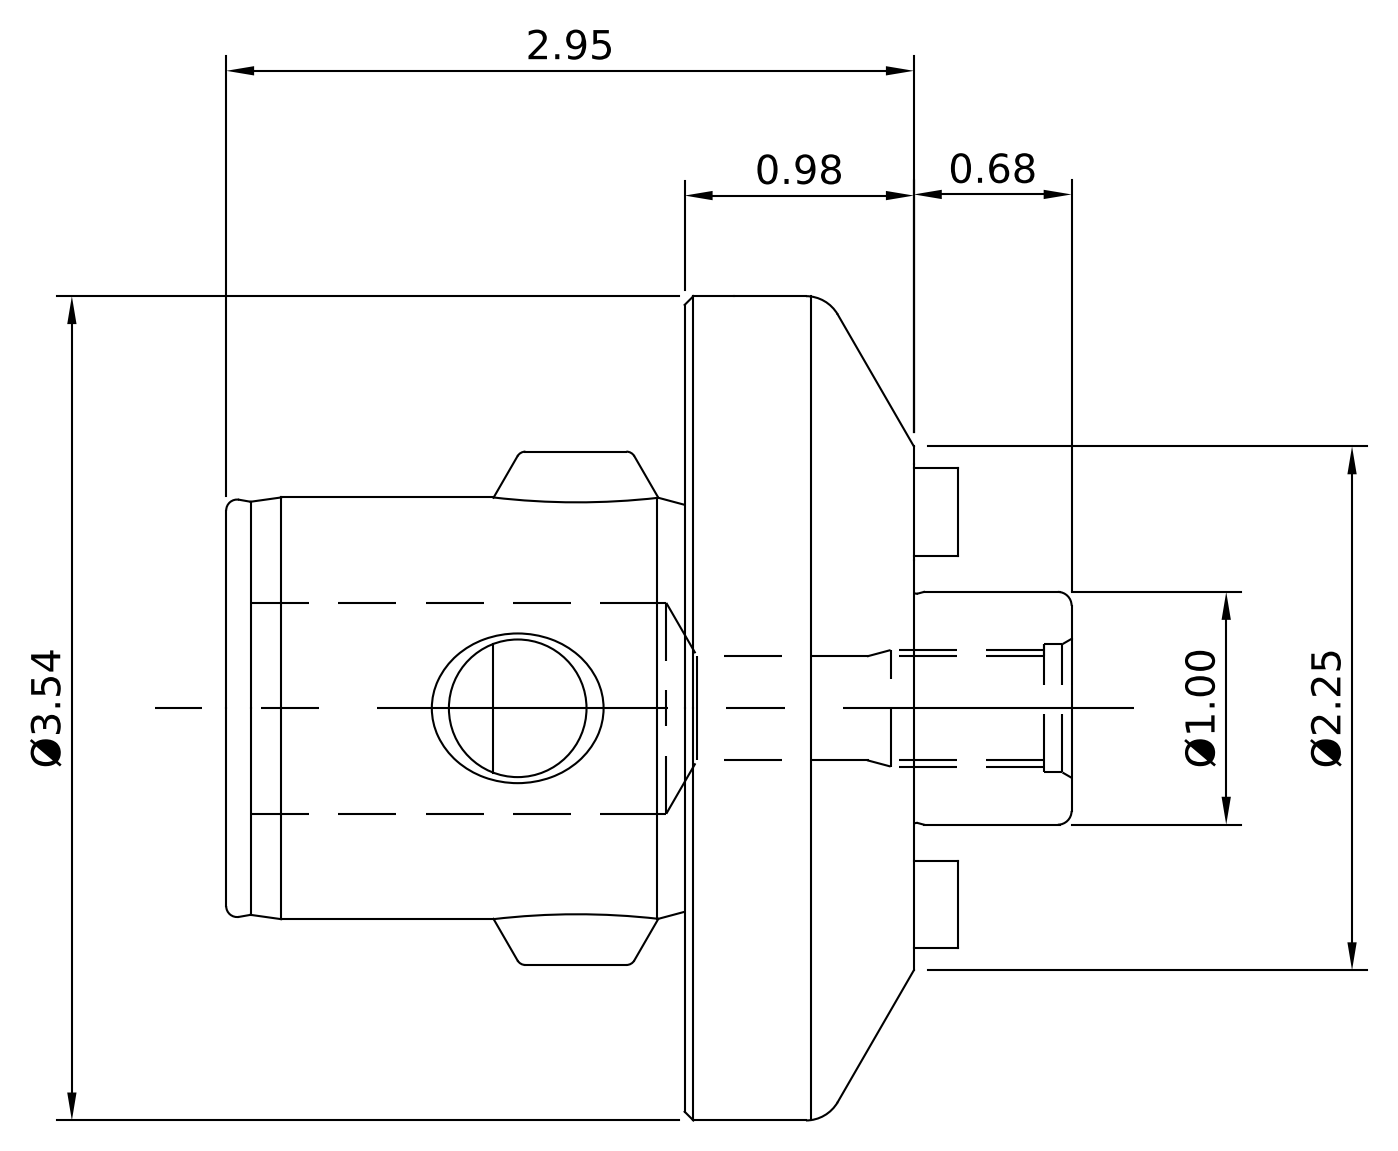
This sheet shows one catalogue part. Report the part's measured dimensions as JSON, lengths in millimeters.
{"part_name": "691-50XRing_10.691.507Ring; 10.691.50X_10.691.507; 11.690.711; 11.691.622 (+1 more)", "step_written_by": "SolidWorks 2010 (CONFIG_CONTROL_DESIGN)", "units": "millimeters", "bodies": {"solids": 6, "faces": 260, "planar": 56, "cylindrical": 79, "other": 125}, "overall_size": [103.58, 90, 90], "volume_mm3": 220021, "surface_area_mm2": 40723, "round_holes": [[9.52, 2], [8.03, 1], [11.51, 1], [14.4, 1], [15, 1], [18, 1], [22, 1], [24.7, 1]], "round_bosses_or_shafts": [[9.53, 2], [90, 1], [46, 1], [30.18, 1], [25.39, 1], [17.9, 1], [15.9, 1], [12.7, 1]], "partial_cylinders_radius": [[23, 1]], "face_to_face_distances": [25, 50, 75, 103.58, 53.58, 28.58, 94.05, 44.05, 19.05, 9.53], "hole_center_spacings": [21.43, 42.86]}
